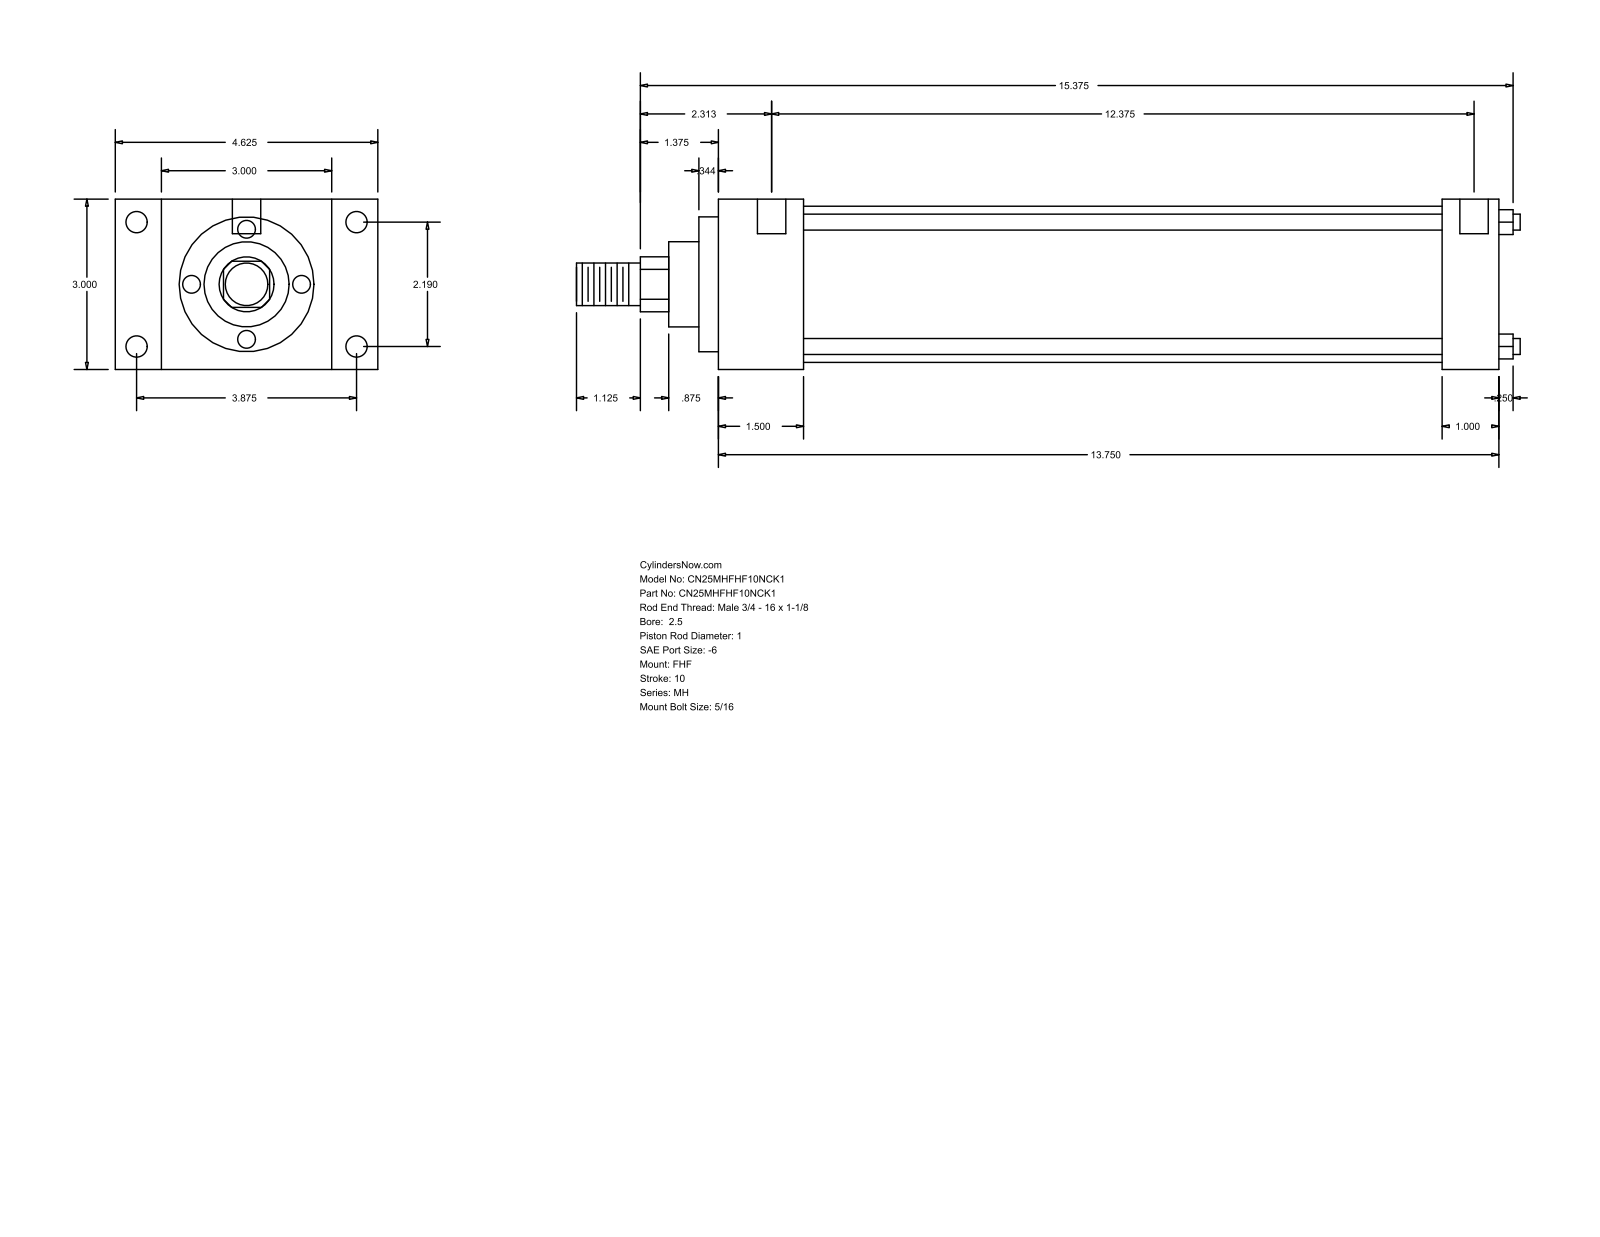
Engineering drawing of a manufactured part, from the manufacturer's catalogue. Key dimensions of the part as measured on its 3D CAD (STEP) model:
Part name (STEP PRODUCT): MH_FHF__0250_1
STEP written by: GSSL Pune (CONFIG_CONTROL_DESIGN)
Units: millimetres
Bodies: 0 solids, 90 faces (61 planar, 29 cylindrical, 0 other)
Overall size (bounding box): 422.27 × 117.47 × 76.2
Round holes (diameter × count): ⌀5.56 ×4, ⌀9.53 ×4, ⌀12.7 ×2
Round bosses / shafts (diameter × count): ⌀7.14 ×4, ⌀69.85 ×1, ⌀60.33 ×1, ⌀38.1 ×1, ⌀25.4 ×1, ⌀19.05 ×1
Partial cylindrical surfaces — rounded edges, fillets, slot ends (radius × count): R12.29 ×1
Main face-to-face distances: 76.2, 349.26, 38.11, 311.15, 20.64, 96.84, 117.48, 323.85, 285.74, 25.41
Hole centre spacings: 55.62, 98.42, 113.05, 322.26, 3.18, 4.76, 314.32, 317.5
